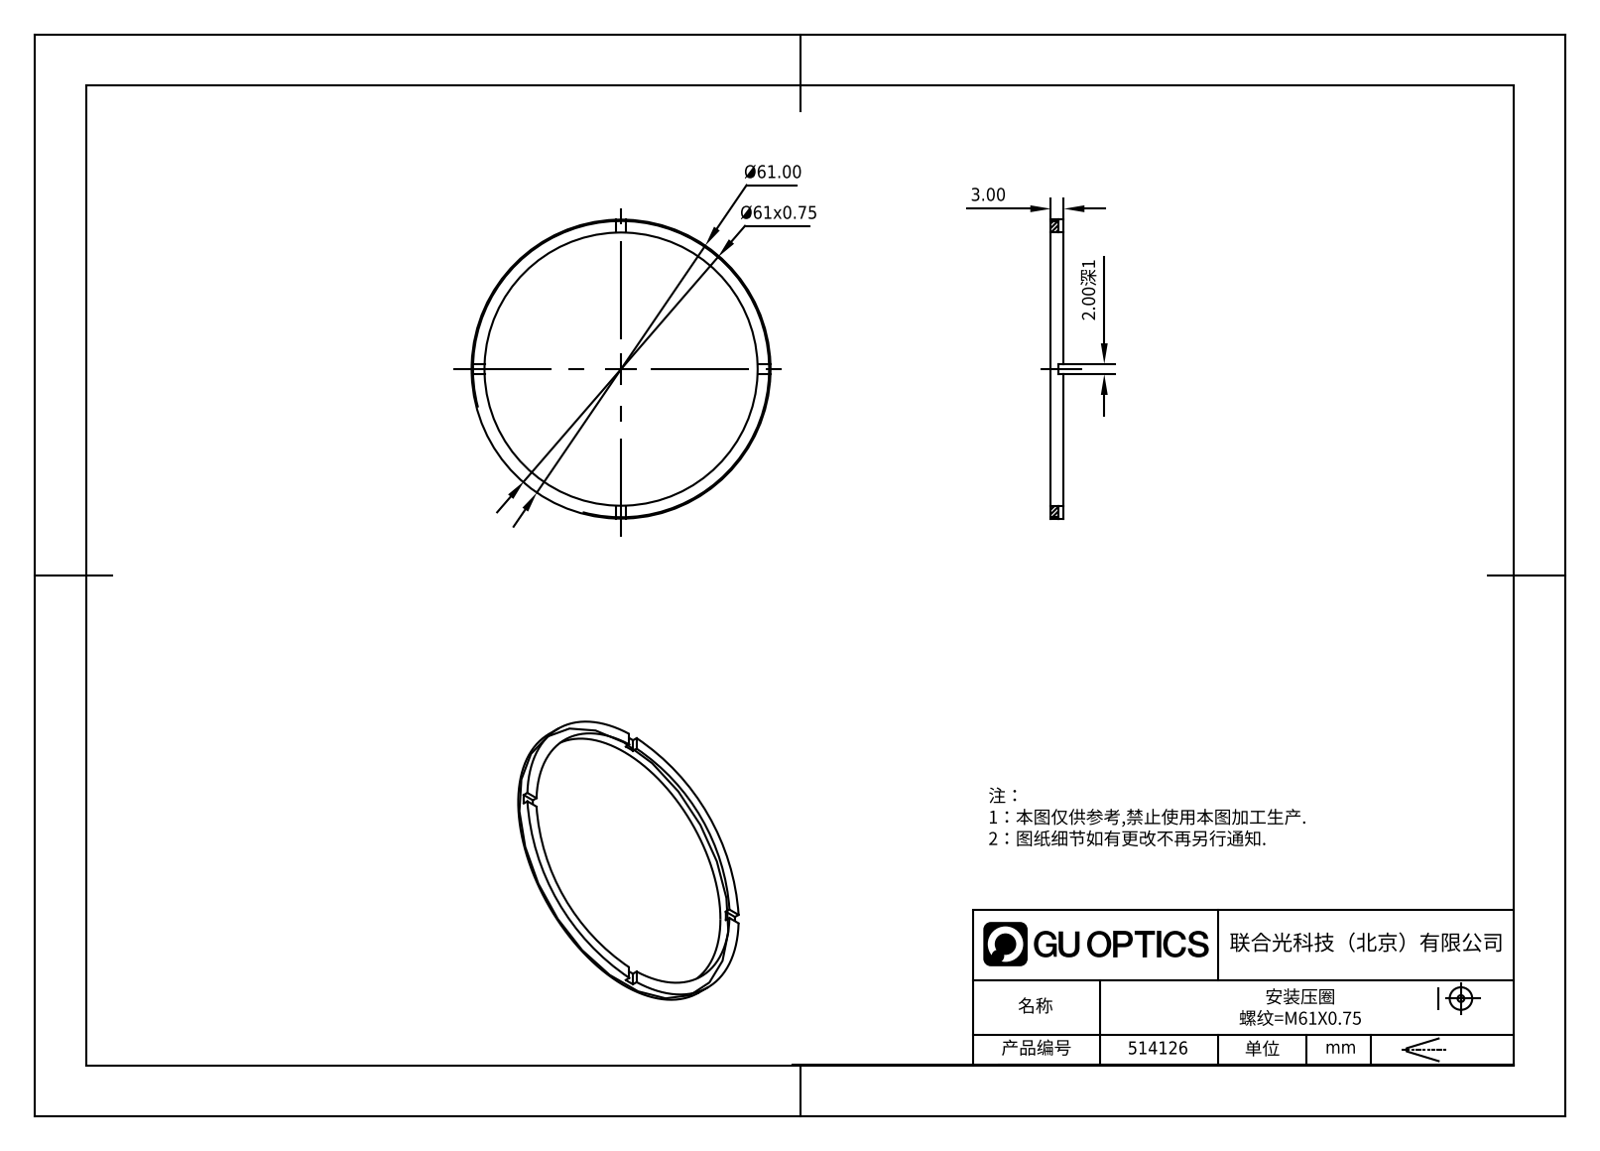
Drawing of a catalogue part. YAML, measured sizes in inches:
part_name: "514126"
step_written_by: "SolidWorks 2020 (CONFIG_CONTROL_DESIGN)"
units: inches
bodies: {solids: 1, faces: 21, planar: 17, cylindrical: 4, other: 0}
overall_size: [2.402, 2.402, 0.118]
volume: 0.083
surface_area: 3.14
round_holes:
  - {diameter: 2.205, count: 1}
round_bosses_or_shafts:
  - {diameter: 2.402, count: 1}
face_to_face_distances: [0.118, 0.079, 0.039]
